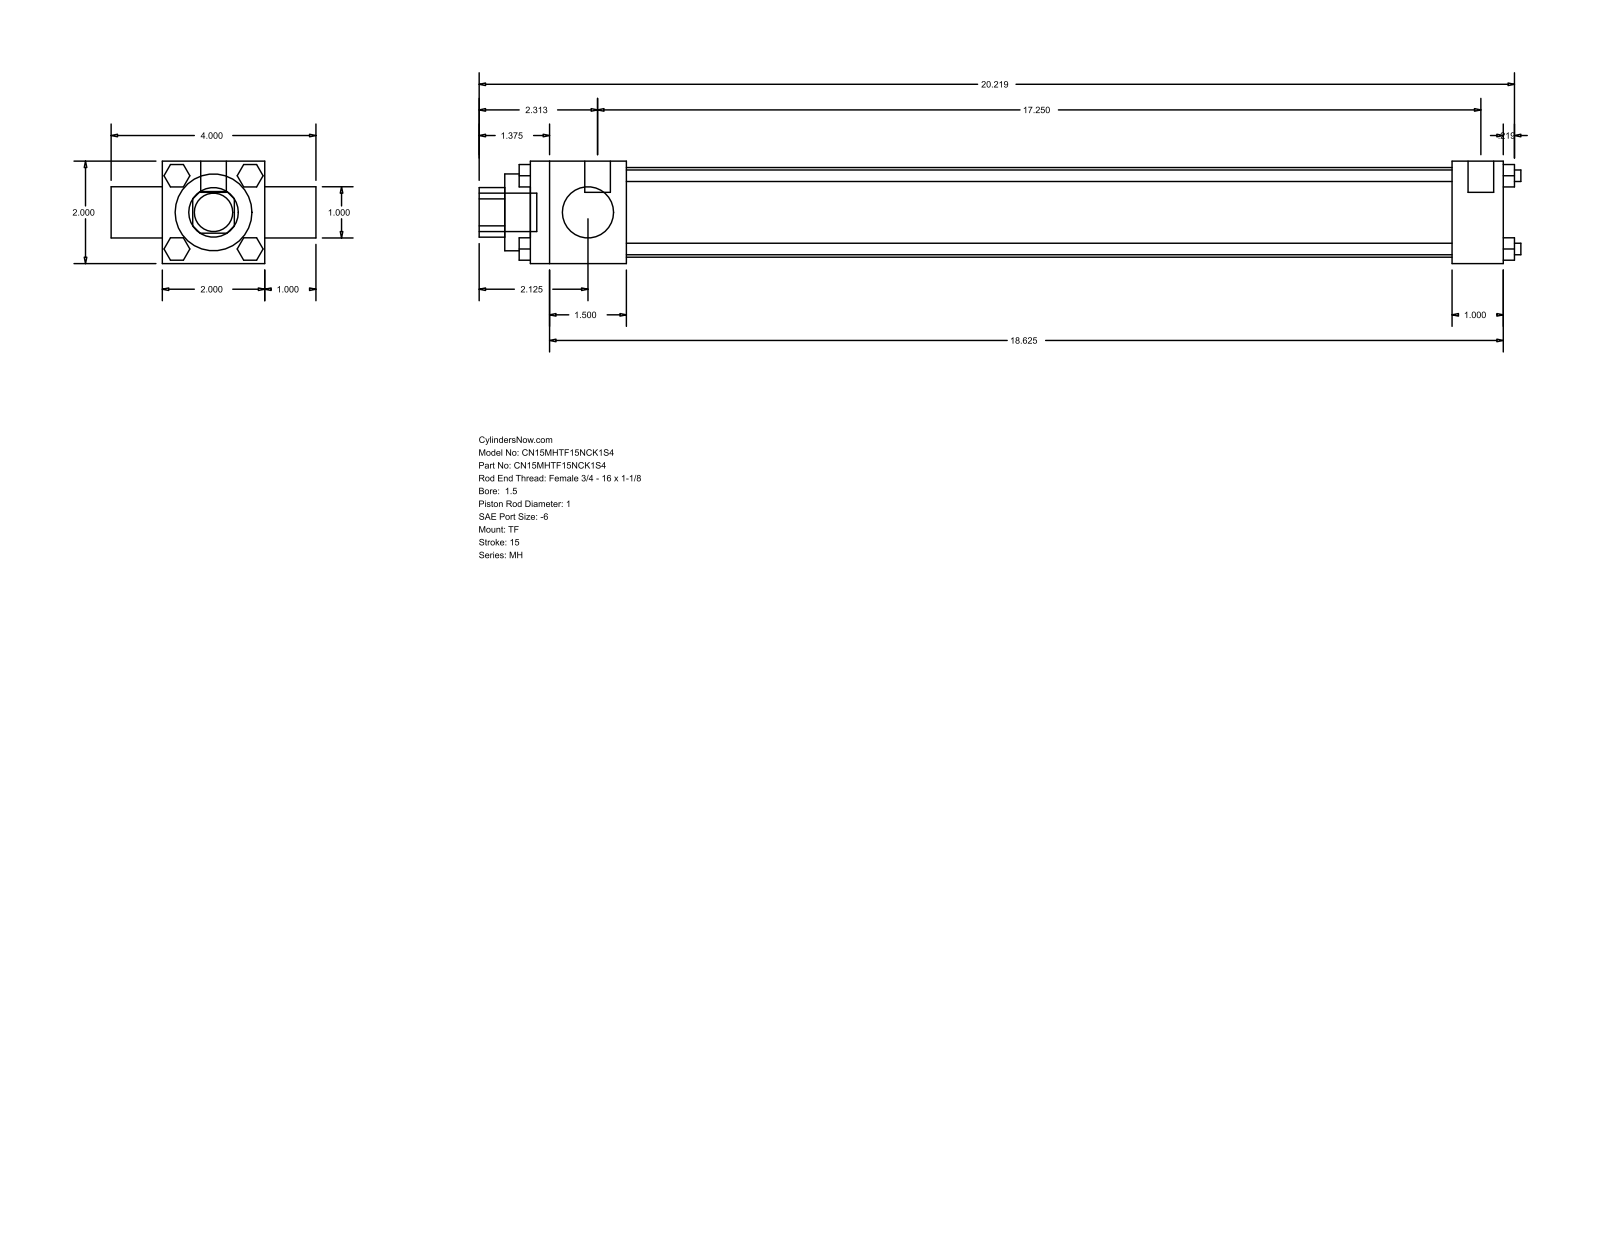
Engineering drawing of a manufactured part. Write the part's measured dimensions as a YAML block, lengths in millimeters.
part_name: "MH_TF__0150_1"
step_written_by: "GSSL Pune (CONFIG_CONTROL_DESIGN)"
units: millimeters
bodies: {solids: 0, faces: 120, planar: 92, cylindrical: 28, other: 0}
overall_size: [516.73, 101.6, 50.8]
round_holes:
  - {diameter: 25.4, count: 2}
  - {diameter: 38.1, count: 1}
  - {diameter: 44.45, count: 1}
round_bosses_or_shafts:
  - {diameter: 5.71, count: 4}
  - {diameter: 5.56, count: 3}
  - {diameter: 12.7, count: 2}
  - {diameter: 19.05, count: 1}
partial_cylinders:
  - {radius: 12.29, count: 1}
face_to_face_distances: [50.8, 25.4, 482.6, 76.2, 47.63, 434.97, 457.2, 409.57, 488.16, 12.7]
